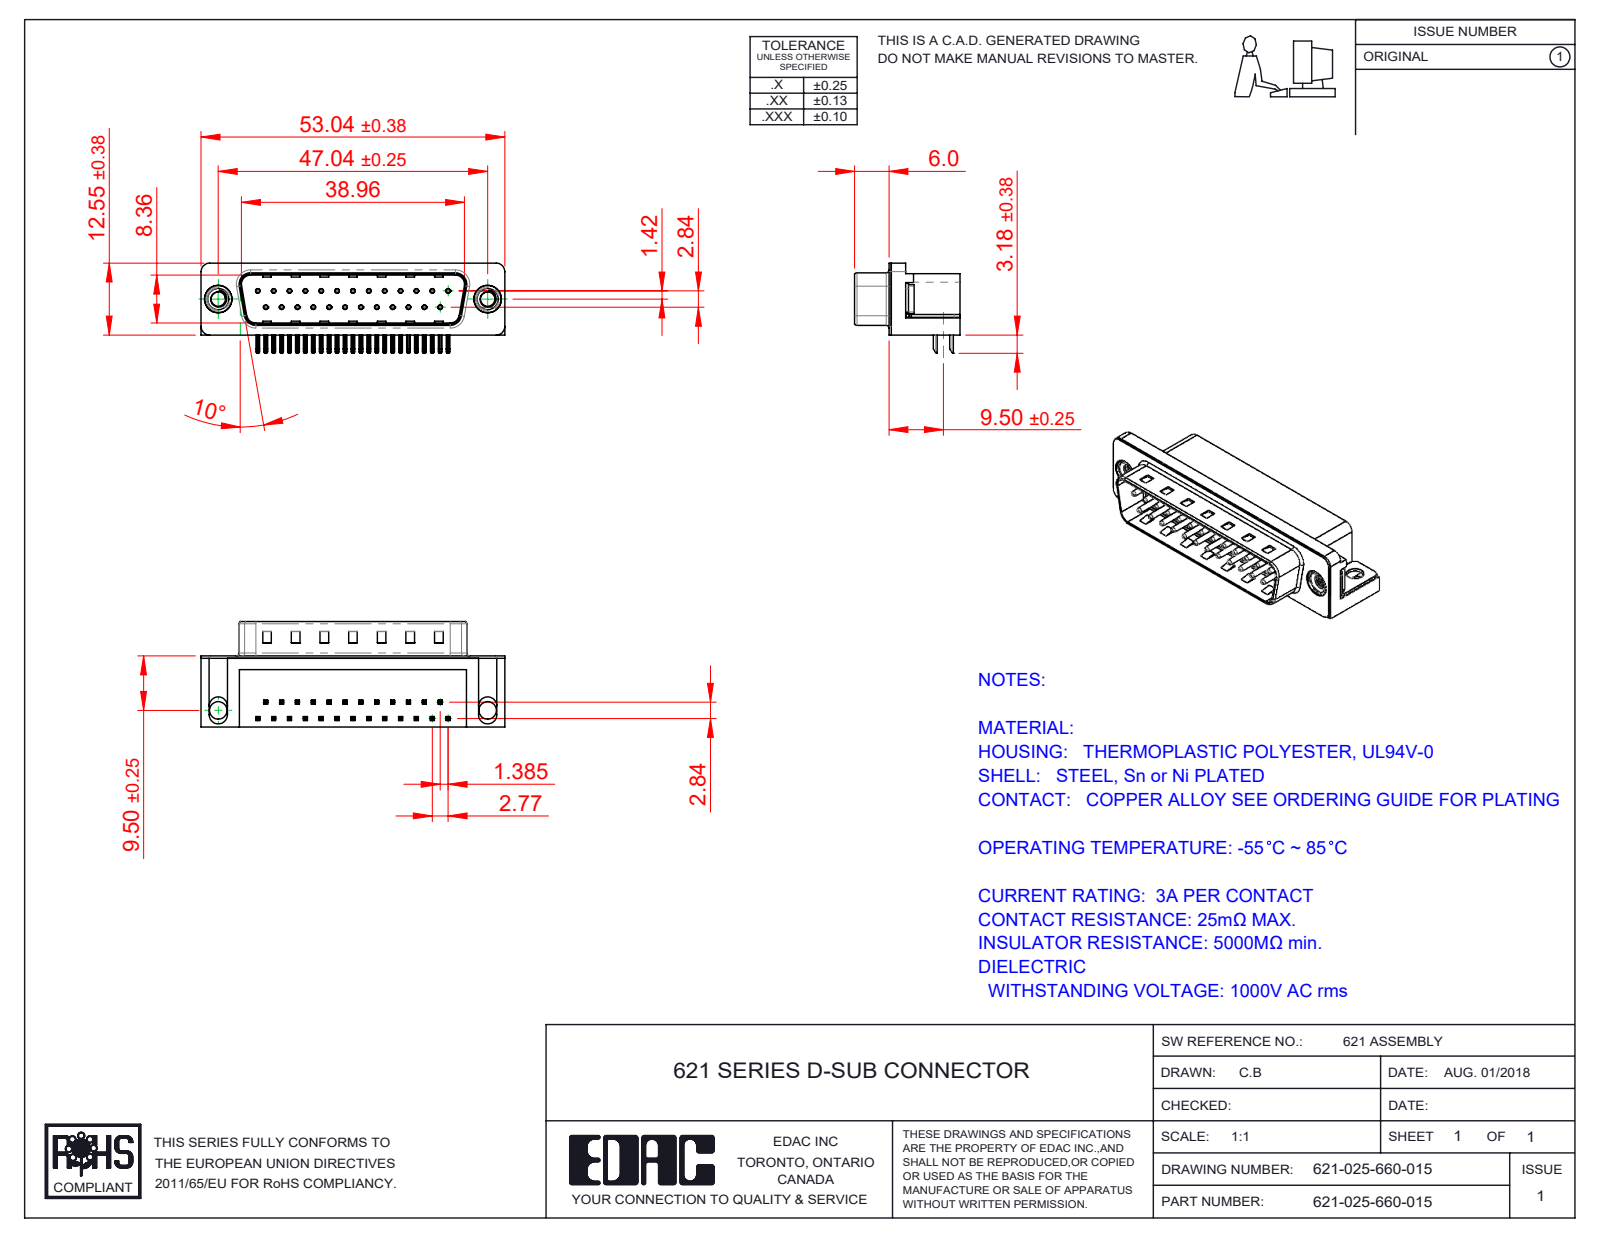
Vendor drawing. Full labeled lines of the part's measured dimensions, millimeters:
Part name (STEP PRODUCT): 621 Contact Top; 621-025-660-015; 621 Housing_25 Socket; 621 Shell_25 Socket (+3 more)
STEP written by: SolidWorks 2016 (CONFIG_CONTROL_DESIGN)
Units: millimetres
Bodies: 31 solids, 2261 faces (1403 planar, 663 cylindrical, 195 other)
Overall size (bounding box): 53.04 × 18.4 × 15.73
Volume: 6 340 mm³ · Surface area: 7 673 mm²
Round holes (diameter × count): ⌀0.35 ×25, ⌀0.8 ×25, ⌀2.5 ×2, ⌀3.05 ×2, ⌀4 ×2, ⌀4.8 ×2, ⌀5 ×2
Round bosses / shafts (diameter × count): ⌀0.75 ×25, ⌀4.9 ×2, ⌀4.75 ×2, ⌀3.9 ×2
Partial cylindrical surfaces — rounded edges, fillets, slot ends (radius × count): R0.25 ×108, R0.12 ×50, R1 ×16, R0.5 ×9, R1.6 ×8, R1.5 ×7, R0.9 ×4, R2 ×4
Main face-to-face distances: 0.4, 12, 10.35, 2.1, 8.76, 10.46, 1.7, 10.86, 12.4, 9
Hole centre spacings: 3.16, 2.77, 5.54, 8.31, 11.08, 13.85, 16.62, 5.03
